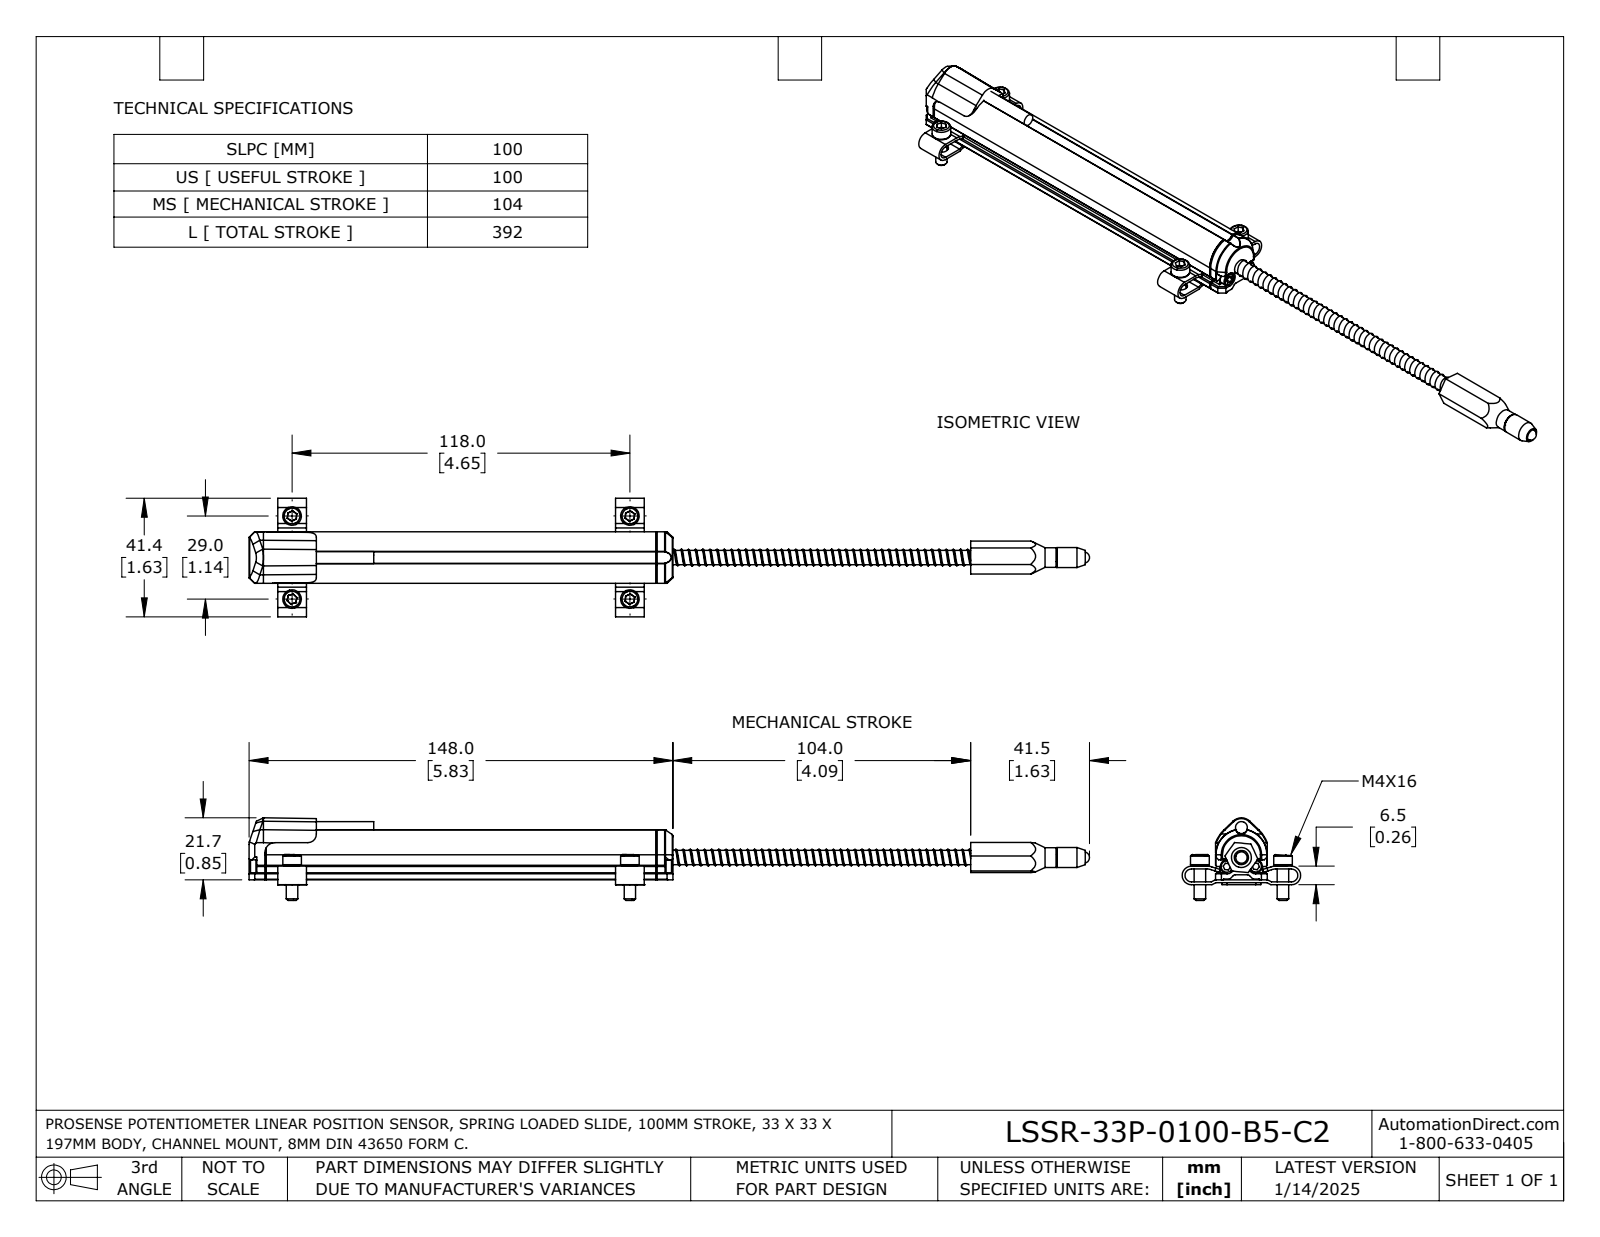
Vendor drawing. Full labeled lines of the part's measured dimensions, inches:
Part name (STEP PRODUCT): LSSR-33P-0100-B5-C2
STEP written by: SolidWorks 2023 (AUTOMOTIVE_DESIGN)
Units: inches
Bodies: 22 solids, 610 faces (374 planar, 173 cylindrical, 63 other)
Overall size (bounding box): 11.555 × 1.63 × 1.136
Volume: 2.838 in³ · Surface area: 40.19 in²
Round holes (diameter × count): ⌀0.177 ×4, ⌀0.197 ×4, ⌀0.102 ×2, ⌀0.104 ×2, ⌀0.157 ×1, ⌀0.213 ×1, ⌀0.27 ×1, ⌀0.272 ×1, ⌀0.335 ×1
Round bosses / shafts (diameter × count): ⌀0.256 ×4, ⌀0.157 ×4, ⌀0.181 ×3, ⌀0.113 ×3, ⌀0.059 ×2, ⌀0.276 ×1, ⌀0.197 ×1, ⌀0.165 ×1
Partial cylindrical surfaces — rounded edges, fillets, slot ends (radius × count): R0.008 ×8, R0.059 ×8, R0.004 ×6, R0.02 ×6, R0.012 ×4, R0.049 ×4, R0.069 ×4, R0.089 ×4
Main face-to-face distances: 0.028, 0.709, 0.039, 0.02, 5.374, 0.394, 0.071, 0.098, 0.138, 0.063
Hole centre spacings: 0.231, 1.142, 4.646, 4.784, 0.394
